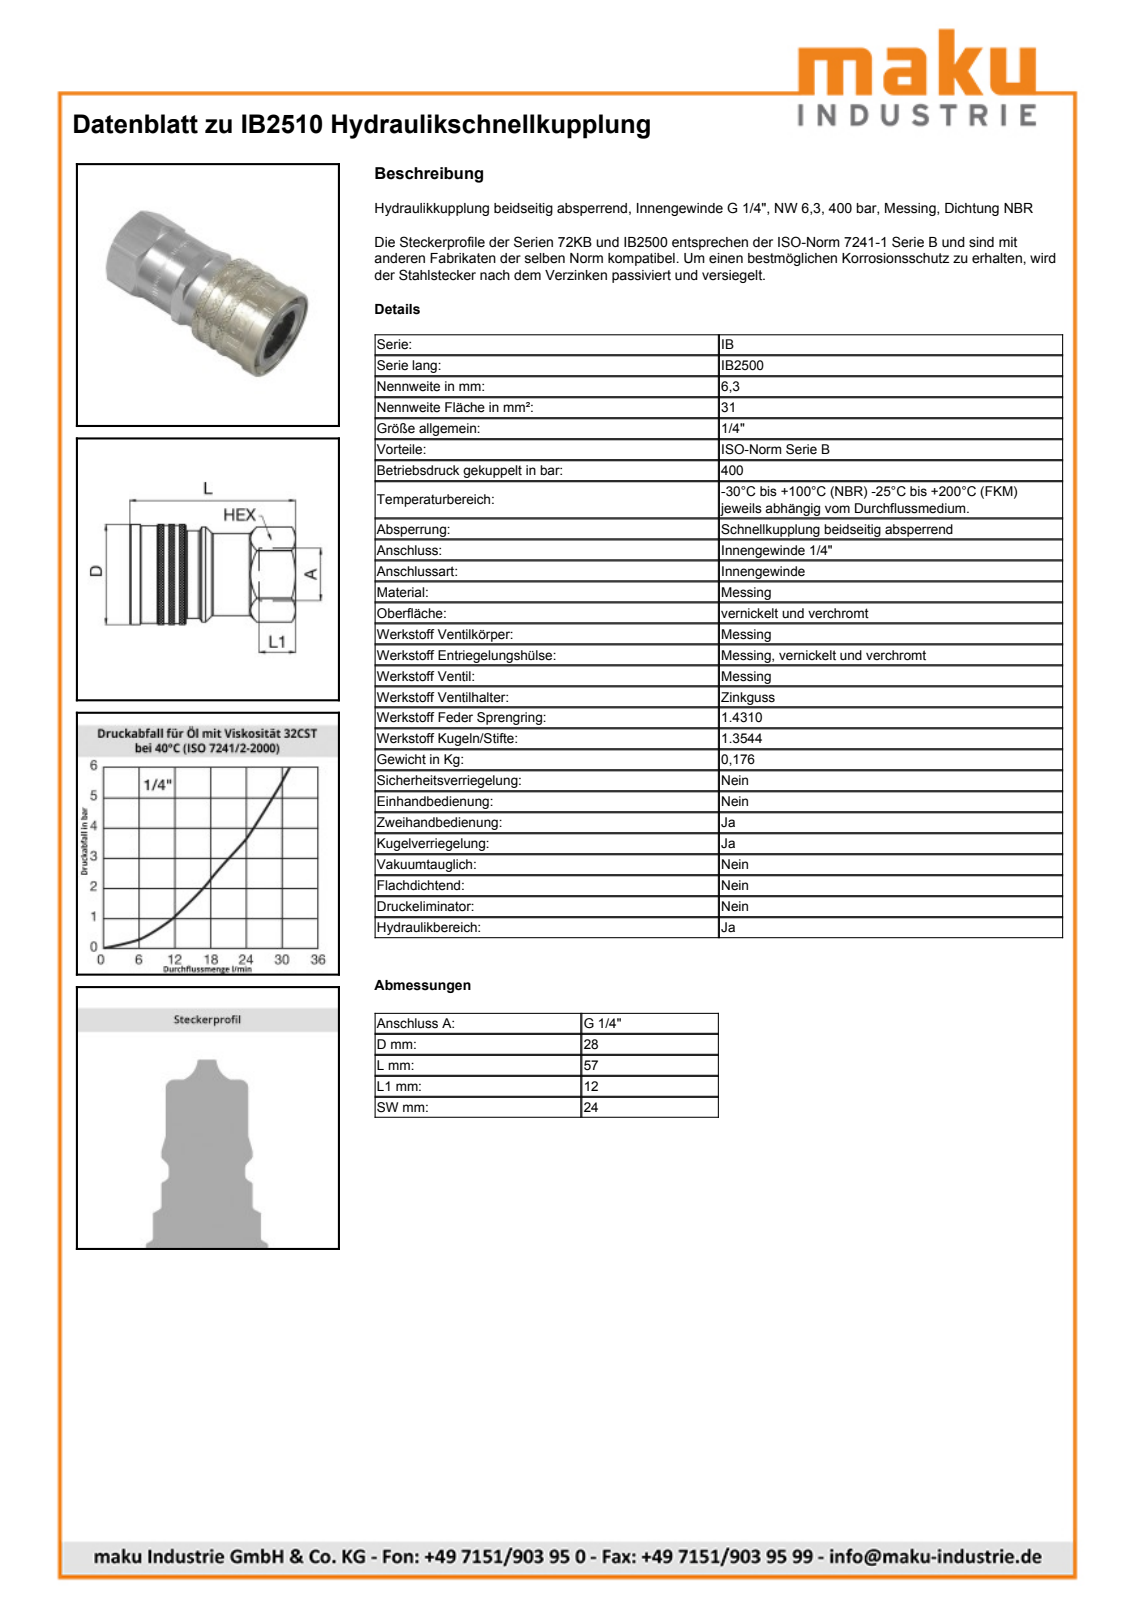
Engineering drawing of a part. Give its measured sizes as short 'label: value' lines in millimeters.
name: IB2510
written by: SolidWorks 2009 (AUTOMOTIVE_DESIGN)
unit: mm
bodies: 2 solids, 250 faces (37 planar, 73 cylindrical, 140 other)
size: 57 × 28 × 28
volume: 23 749 mm³; area: 9 220 mm²
holes: 1× ⌀8, 1× ⌀11.44, 1× ⌀14.3, 1× ⌀14.4, 1× ⌀15.8, 1× ⌀15.9, 1× ⌀21.3, 1× ⌀24.3, 1× ⌀25.7
bosses: 1× ⌀28, 1× ⌀26.8, 1× ⌀26.7, 1× ⌀23.6, 1× ⌀21.2, 1× ⌀19.7
rounds: 1× R8.37, 1× R12.1, 1× R13.3
face distances: 24, 4.3, 2, 11.5, 34.35, 22.85, 57, 45.5, 22.65, 35
